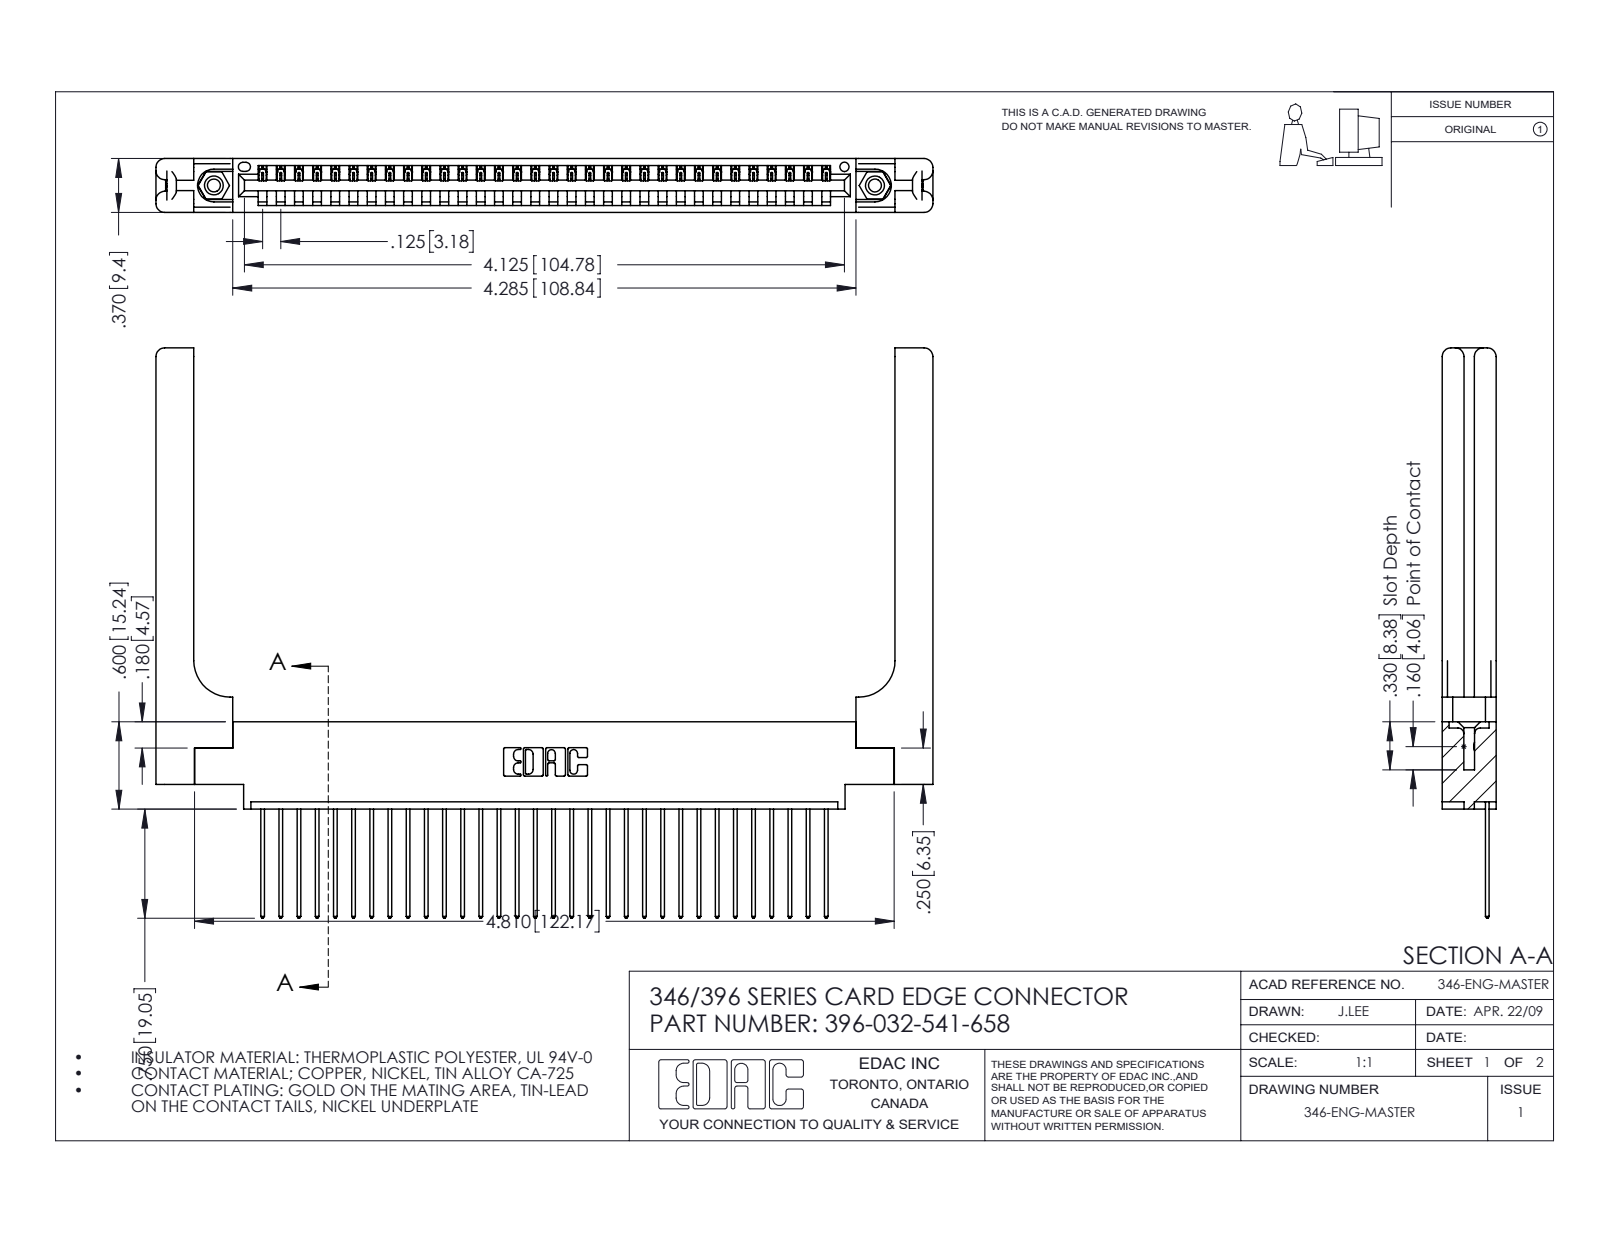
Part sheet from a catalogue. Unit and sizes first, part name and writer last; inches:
Units: inches
Overall size (bounding box): 5.341 × 3.92 × 0.37
Round holes (diameter × count): ⌀0.089 ×2, ⌀0.125 ×2, ⌀0.156 ×2, ⌀0.064 ×1
Round bosses / shafts (diameter × count): ⌀0.155 ×2
Partial cylindrical surfaces — rounded edges, fillets, slot ends (radius × count): R0.006 ×64, R0.01 ×64, R0.01 ×22, R0.06 ×16, R0.007 ×6, R0.031 ×6, R0.026 ×3, R0.03 ×2
Main face-to-face distances: 0.37, 0.048, 0.322, 0.072, 0.148, 0.15, 0.298, 0.025, 0.25, 0.222
Hole centre spacings: 0.246, 4.337, 4.545
Volume: 1.244 in³ · Surface area: 34 in²
Bodies: 37 solids, 2238 faces (1508 planar, 670 cylindrical, 60 other)
Part name (STEP PRODUCT): 396-032-541-658; 345-292-001_345-293-141; 346-220-058_345-220-058; 346 Part_0.170 Offset - 0.156 Dia-TH (+1 more)
STEP written by: SolidWorks 2016 (CONFIG_CONTROL_DESIGN)
